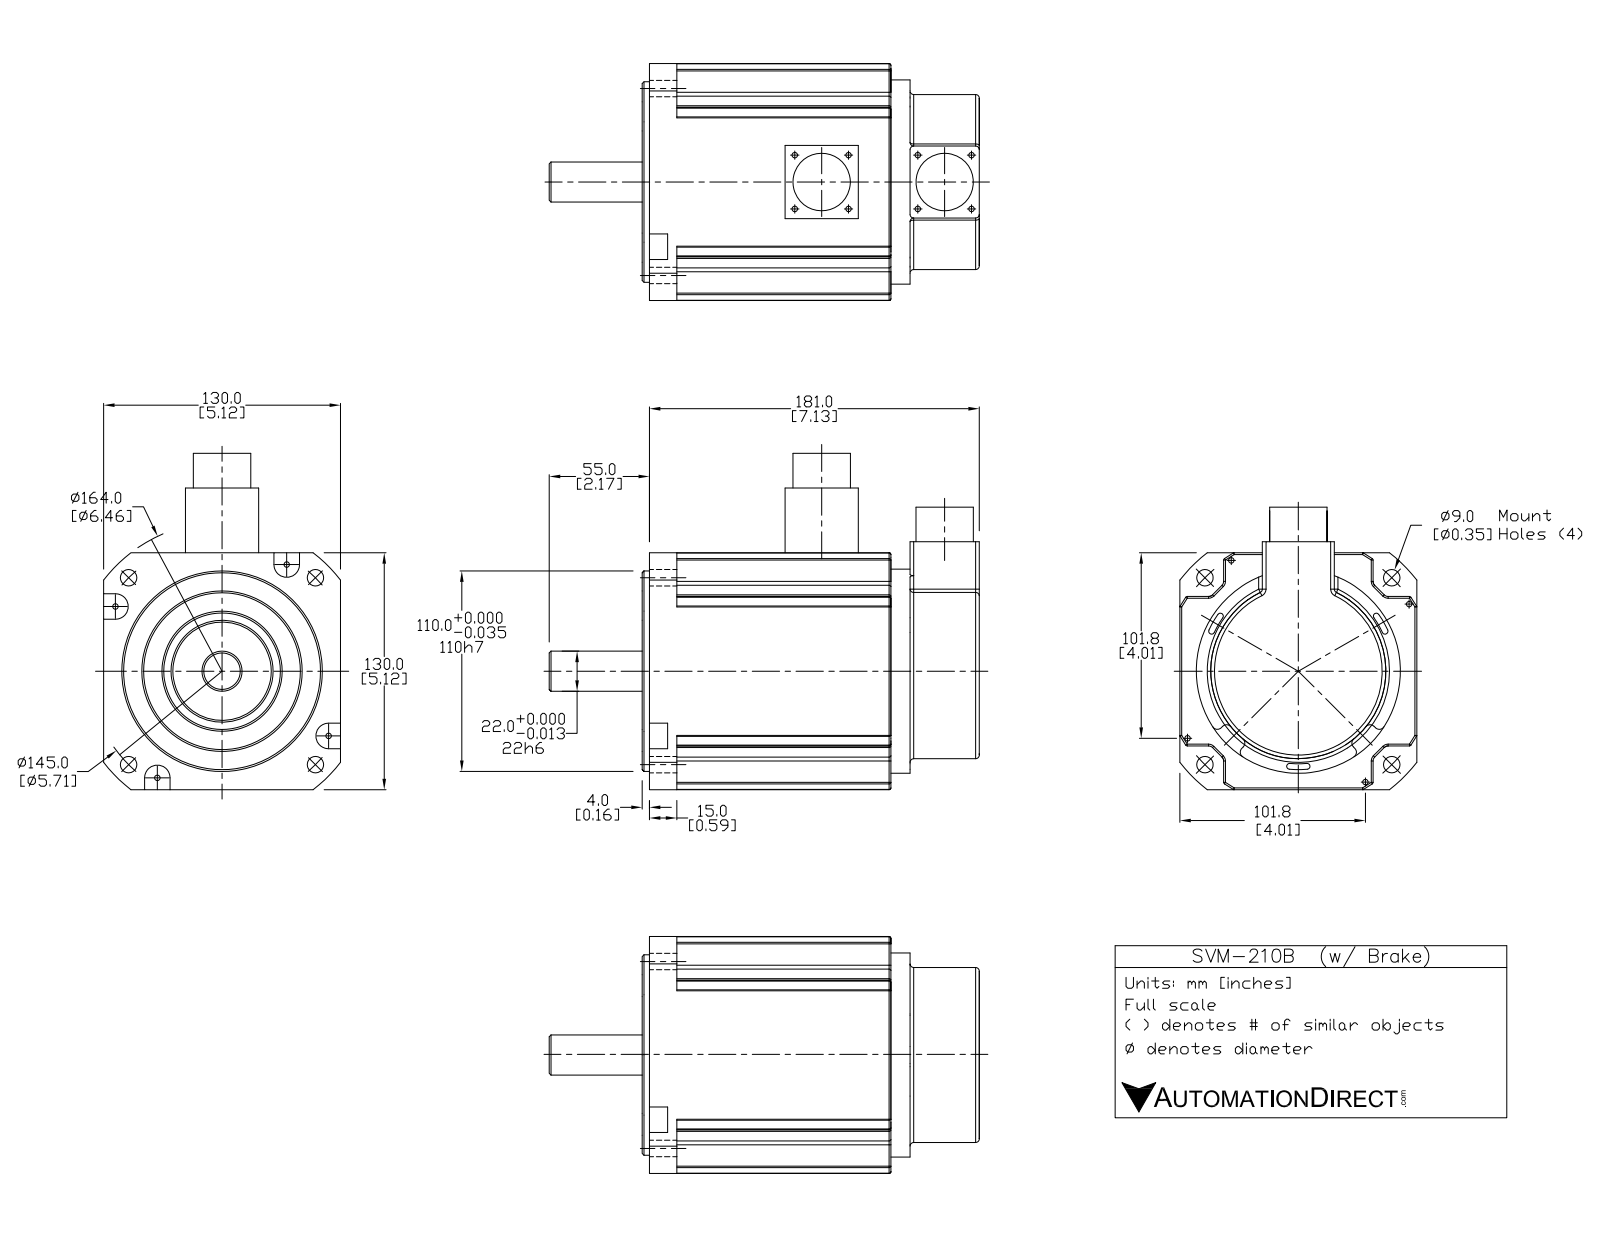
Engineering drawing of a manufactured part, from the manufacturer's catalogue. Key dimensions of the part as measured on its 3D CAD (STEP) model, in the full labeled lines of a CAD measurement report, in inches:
Part name (STEP PRODUCT): SVM-210B
STEP written by: SolidWorks 2015 (AUTOMOTIVE_DESIGN)
Units: inches
Bodies: 36 solids, 382 faces (187 planar, 114 cylindrical, 81 other)
Overall size (bounding box): 9.291 × 7.302 × 5.179
Volume: 150.2 in³ · Surface area: 315.2 in²
Round holes (diameter × count): ⌀0.354 ×4, ⌀1.063 ×1, ⌀1.071 ×1, ⌀3.543 ×1
Round bosses / shafts (diameter × count): ⌀0.079 ×17, ⌀0.059 ×6, ⌀0.472 ×4, ⌀0.394 ×4, ⌀0.098 ×3, ⌀1.24 ×2, ⌀4.409 ×1, ⌀4.331 ×1
Partial cylindrical surfaces — rounded edges, fillets, slot ends (radius × count): R0.079 ×4, R0.157 ×4, R0.276 ×4, R3.228 ×1
Main face-to-face distances: 4.272, 5.118, 4.173, 0.945, 3.228, 4.862, 0.591, 2.264, 6.535, 7.126
Hole centre spacings: 2.855, 4.037, 5.709, 2.698
